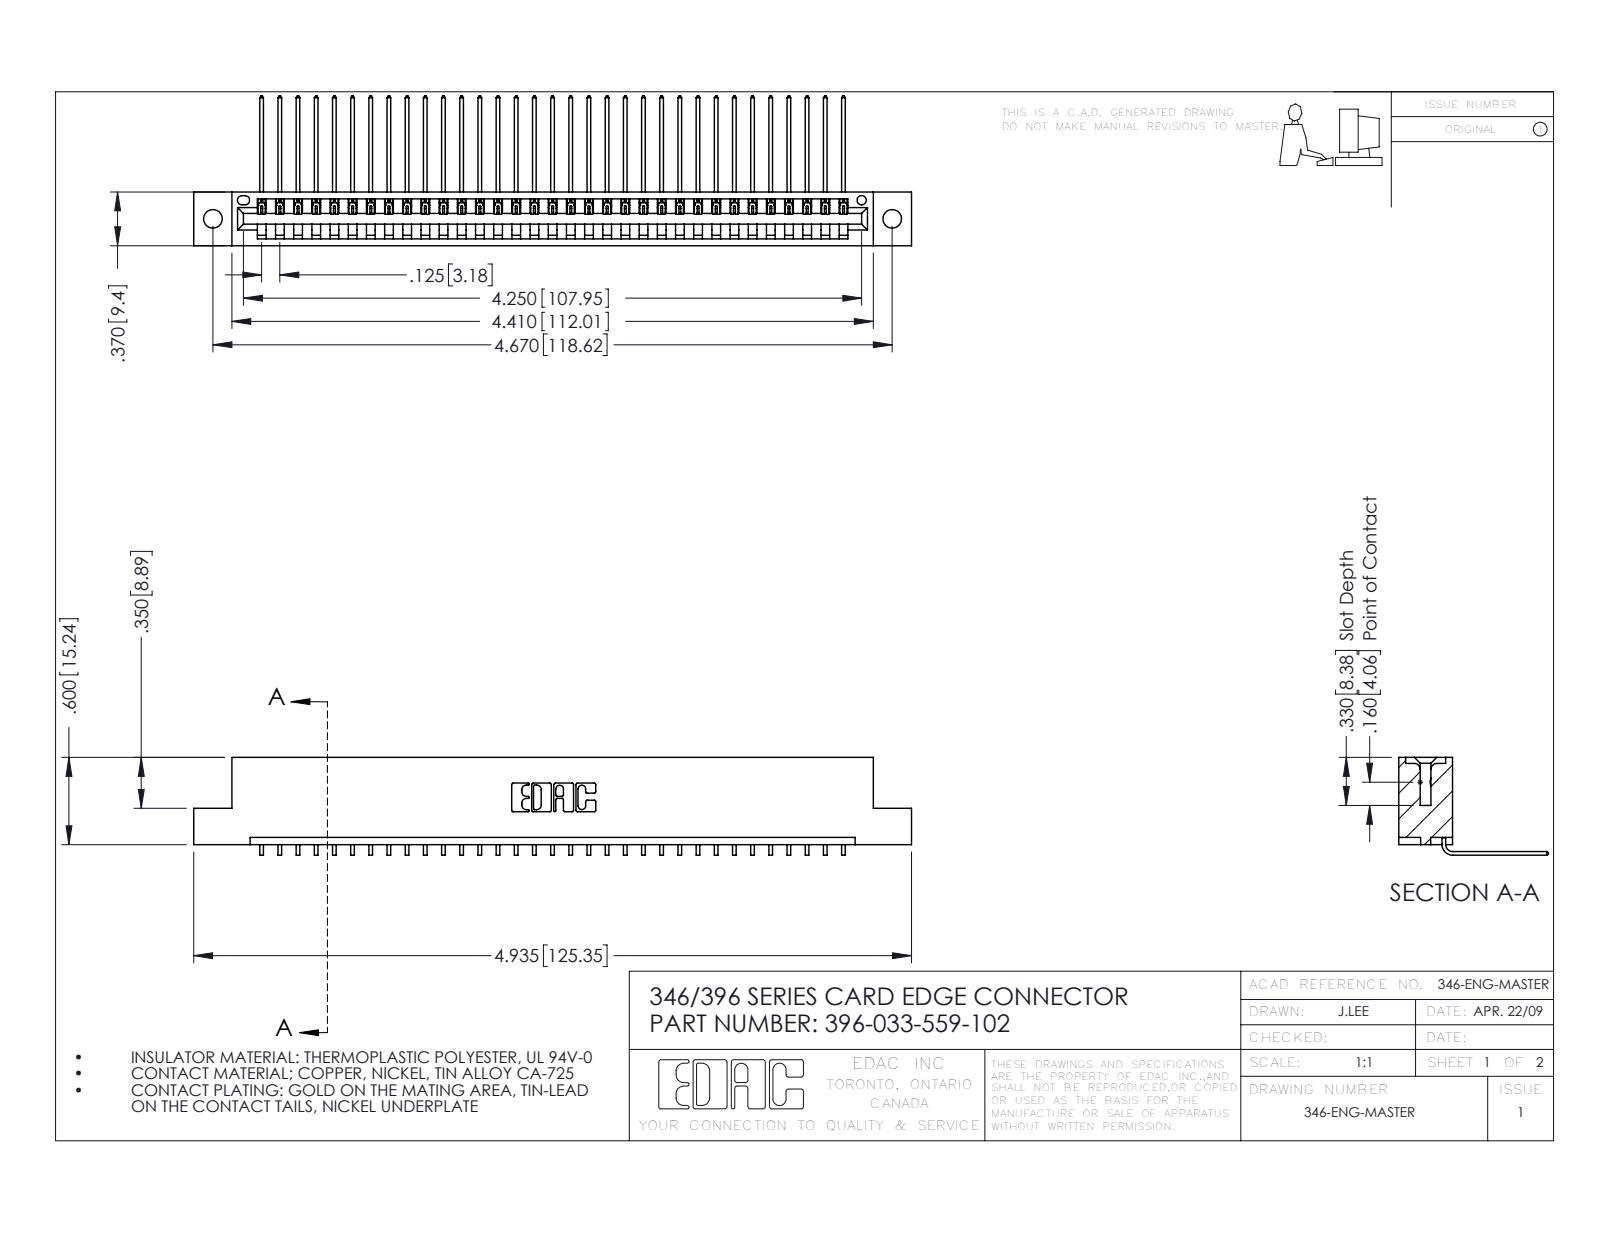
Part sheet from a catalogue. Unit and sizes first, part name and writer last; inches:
Units: inches
Overall size (bounding box): 4.935 × 1.03 × 0.673
Round holes (diameter × count): ⌀0.128 ×2, ⌀0.064 ×1
Partial cylindrical surfaces — rounded edges, fillets, slot ends (radius × count): R0.006 ×66, R0.01 ×22, R0.007 ×6, R0.031 ×6, R0.026 ×3, R0.031 ×2, R0.04 ×2, R0.014 ×1
Main face-to-face distances: 0.048, 0.322, 0.37, 0.25, 0.072, 0.025, 0.298, 0.148, 0.222, 0.1
Hole centre spacings: 0.246, 4.462, 4.67
Volume: 0.733 in³ · Surface area: 23.71 in²
Bodies: 34 solids, 2102 faces (1462 planar, 640 cylindrical, 0 other)
Part name (STEP PRODUCT): 346 Part_Flush Mounting Lugs - 0.128 Dia; 345-292-001_558 559 Tail - 1; 396-033-559-102
STEP written by: SolidWorks 2016 (CONFIG_CONTROL_DESIGN)
